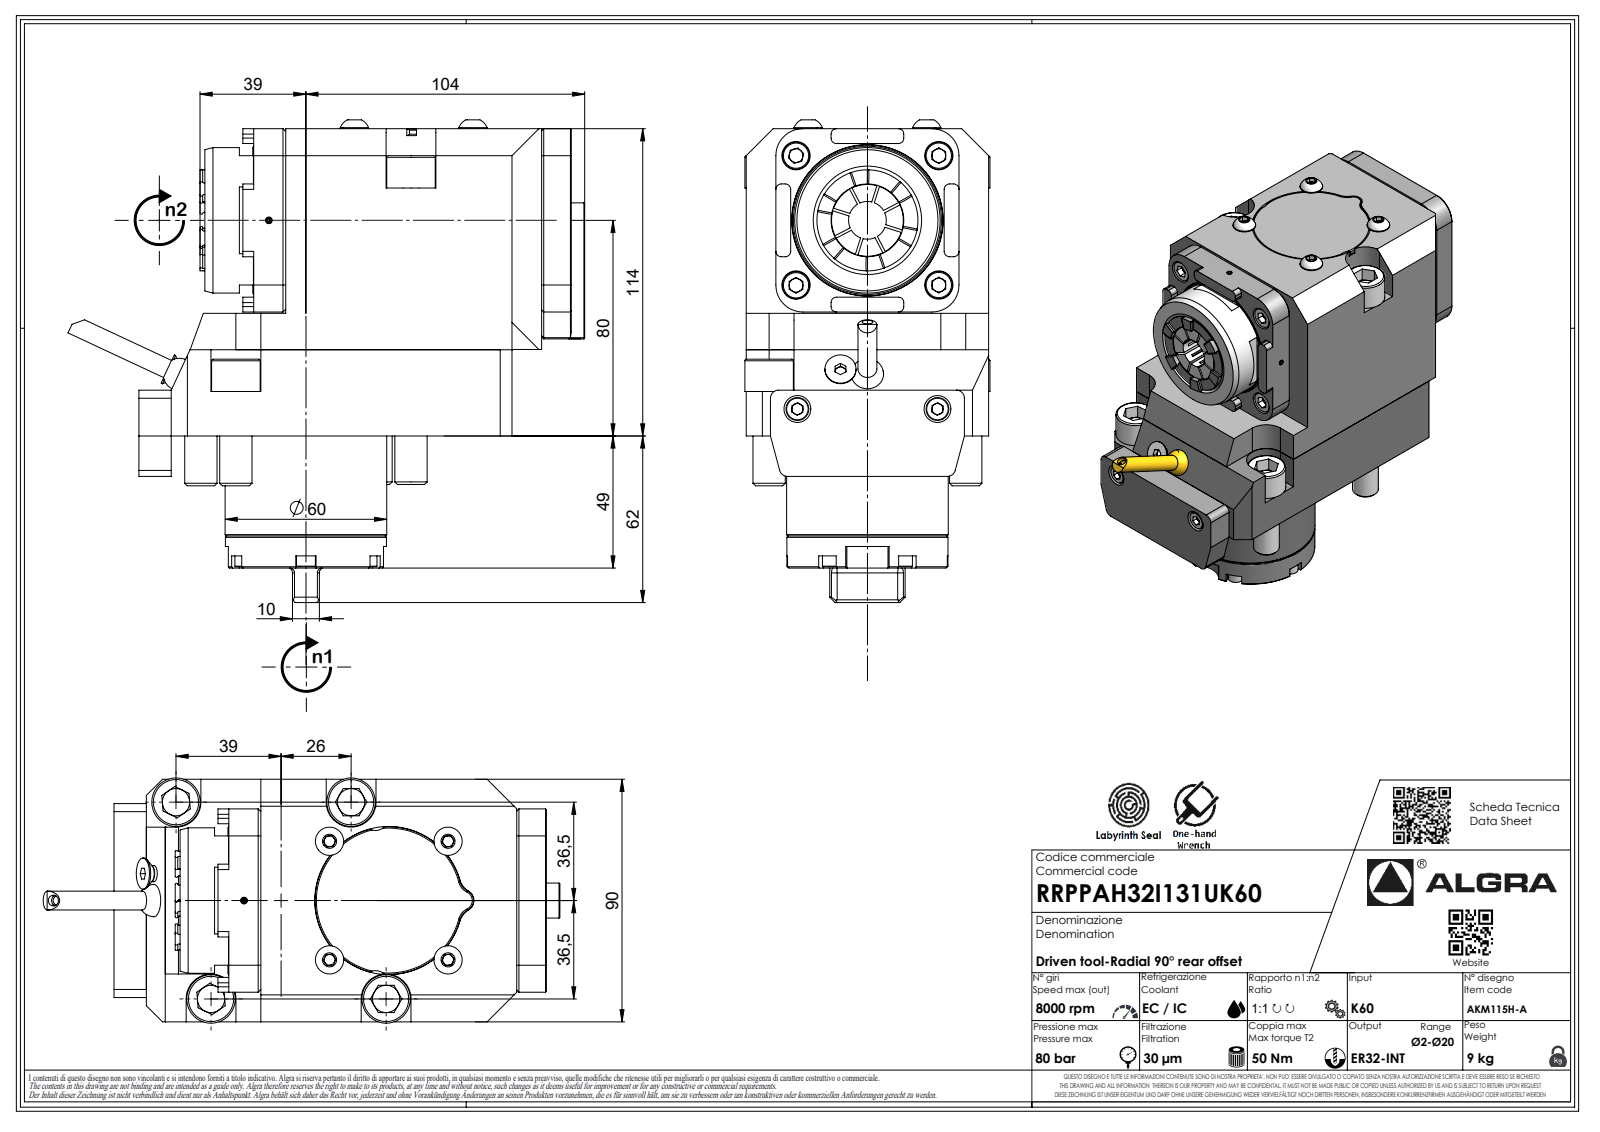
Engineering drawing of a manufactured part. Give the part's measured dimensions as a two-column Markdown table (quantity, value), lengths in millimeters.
| quantity | value |
| --- | --- |
| part name | RRPPAH32I131UK60 |
| STEP written by | SolidWorks 2023 (AUTOMOTIVE_DESIGN) |
| units | millimeters |
| bodies | 1 solid, 590 faces (348 planar, 100 cylindrical, 142 other) |
| overall size | 191.82 × 179.1 × 91 |
| volume | 1 402 000 mm³ |
| surface area | 97 310 mm² |
| round holes (diameter × count) | 2.1 × 1, 4 × 1 |
| round bosses / shafts (diameter × count) | 12 × 4, 10.5 × 4, 18 × 2, 60 × 1, 54 × 1, 7 × 1, 6.37 × 1, 1.7 × 1 |
| partial cylindrical surfaces (radius × count) | 2 × 23, 0.33 × 7, 0.52 × 7, 3.7 × 7, 10 × 6, 3 × 4, 9.25 × 2, 0.21 × 1 |
| main face-to-face distances | 114, 90, 11, 22, 49, 163, 79, 94.5, 45.5, 68.5 |
